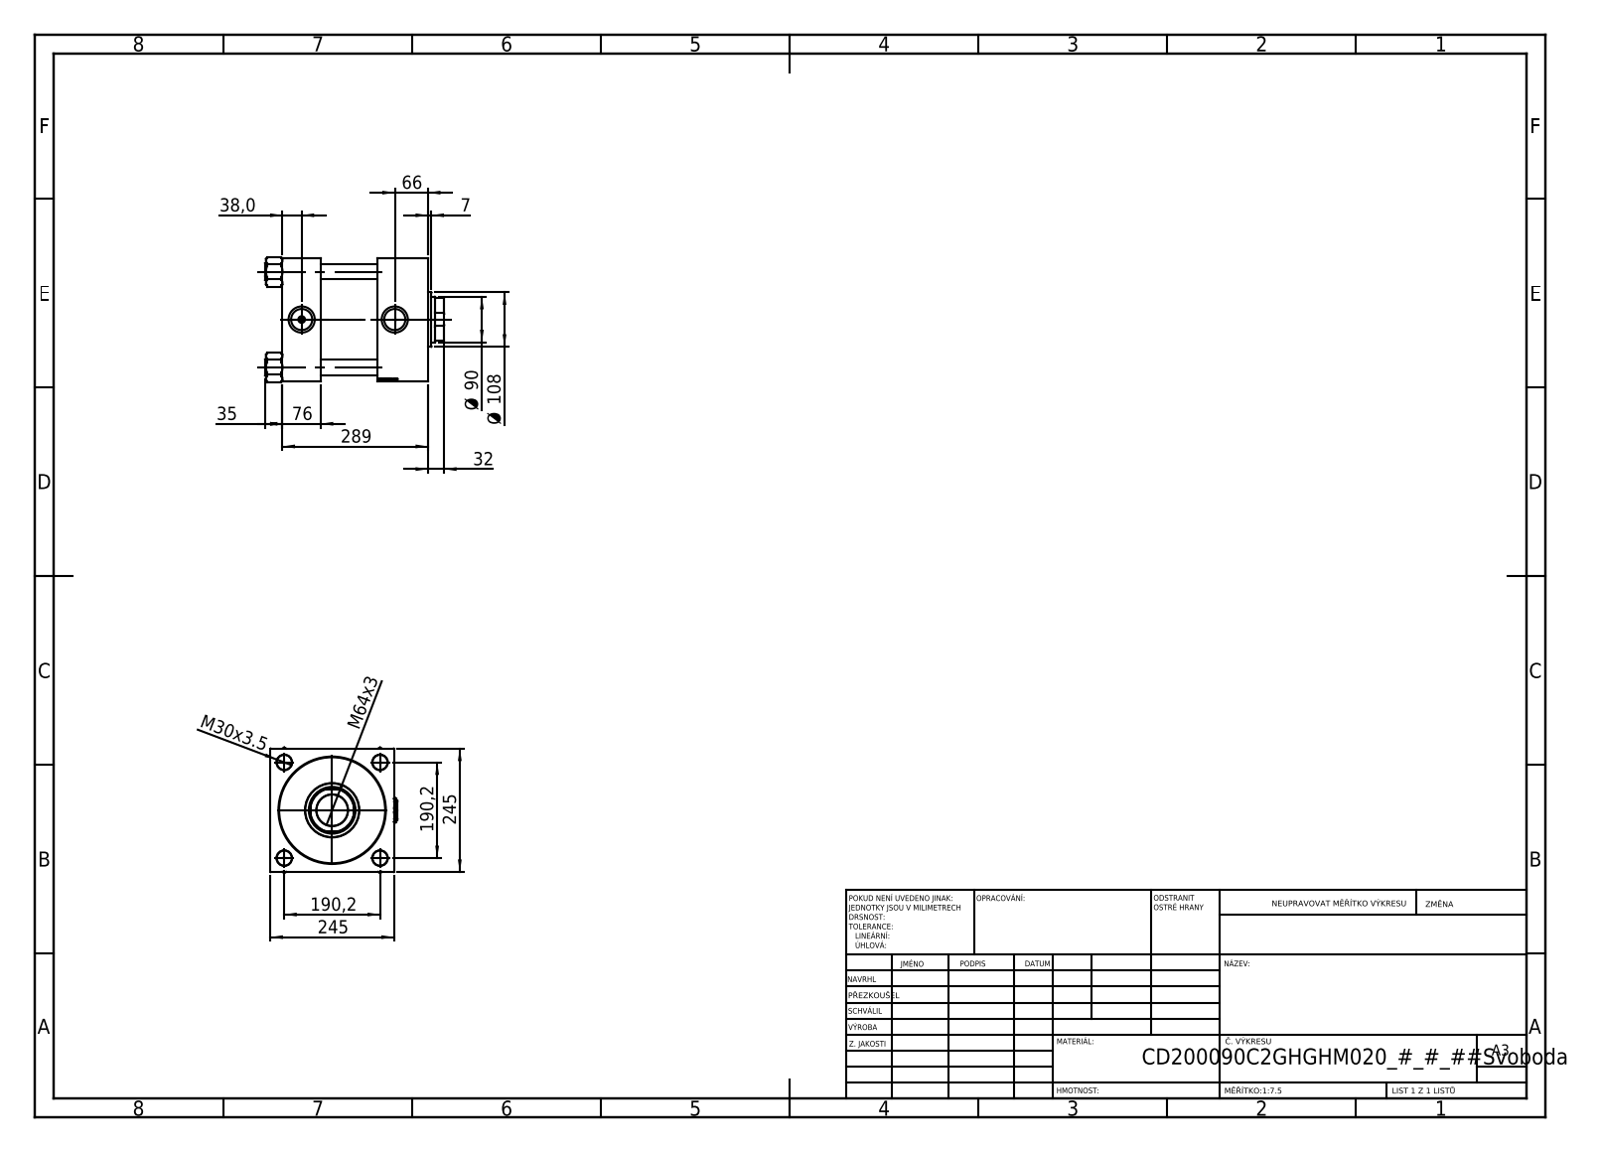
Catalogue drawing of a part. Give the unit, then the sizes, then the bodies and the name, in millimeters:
Units: millimetres
Overall size (bounding box): 356 × 252 × 249.44
Round holes (diameter × count): ⌀30 ×4, ⌀7 ×2, ⌀41.92 ×2, ⌀52 ×2, ⌀62.5 ×1, ⌀90 ×1, ⌀93 ×1, ⌀146 ×1, ⌀200 ×1, ⌀210.5 ×1
Round bosses / shafts (diameter × count): ⌀33 ×4, ⌀206 ×1, ⌀108 ×1
Partial cylindrical surfaces — rounded edges, fillets, slot ends (radius × count): R44 ×1
Main face-to-face distances: 245, 76, 289, 213, 260.3, 184.3, 28.7, 188, 112, 72.3
Hole centre spacings: 134.49, 190.2, 268.98, 185
Volume: 13 430 000 mm³ · Surface area: 1 047 000 mm²
Bodies: 12 solids, 1250 faces (598 planar, 94 cylindrical, 558 other)
Part name (STEP PRODUCT): V215CD_C_TYCINKA; V215CD_VCP_C; Zatka_pro_OIL_PORT; V215CD_Body_C (+2 more)
STEP written by: SolidWorks 2019 (CONFIG_CONTROL_DESIGN)
